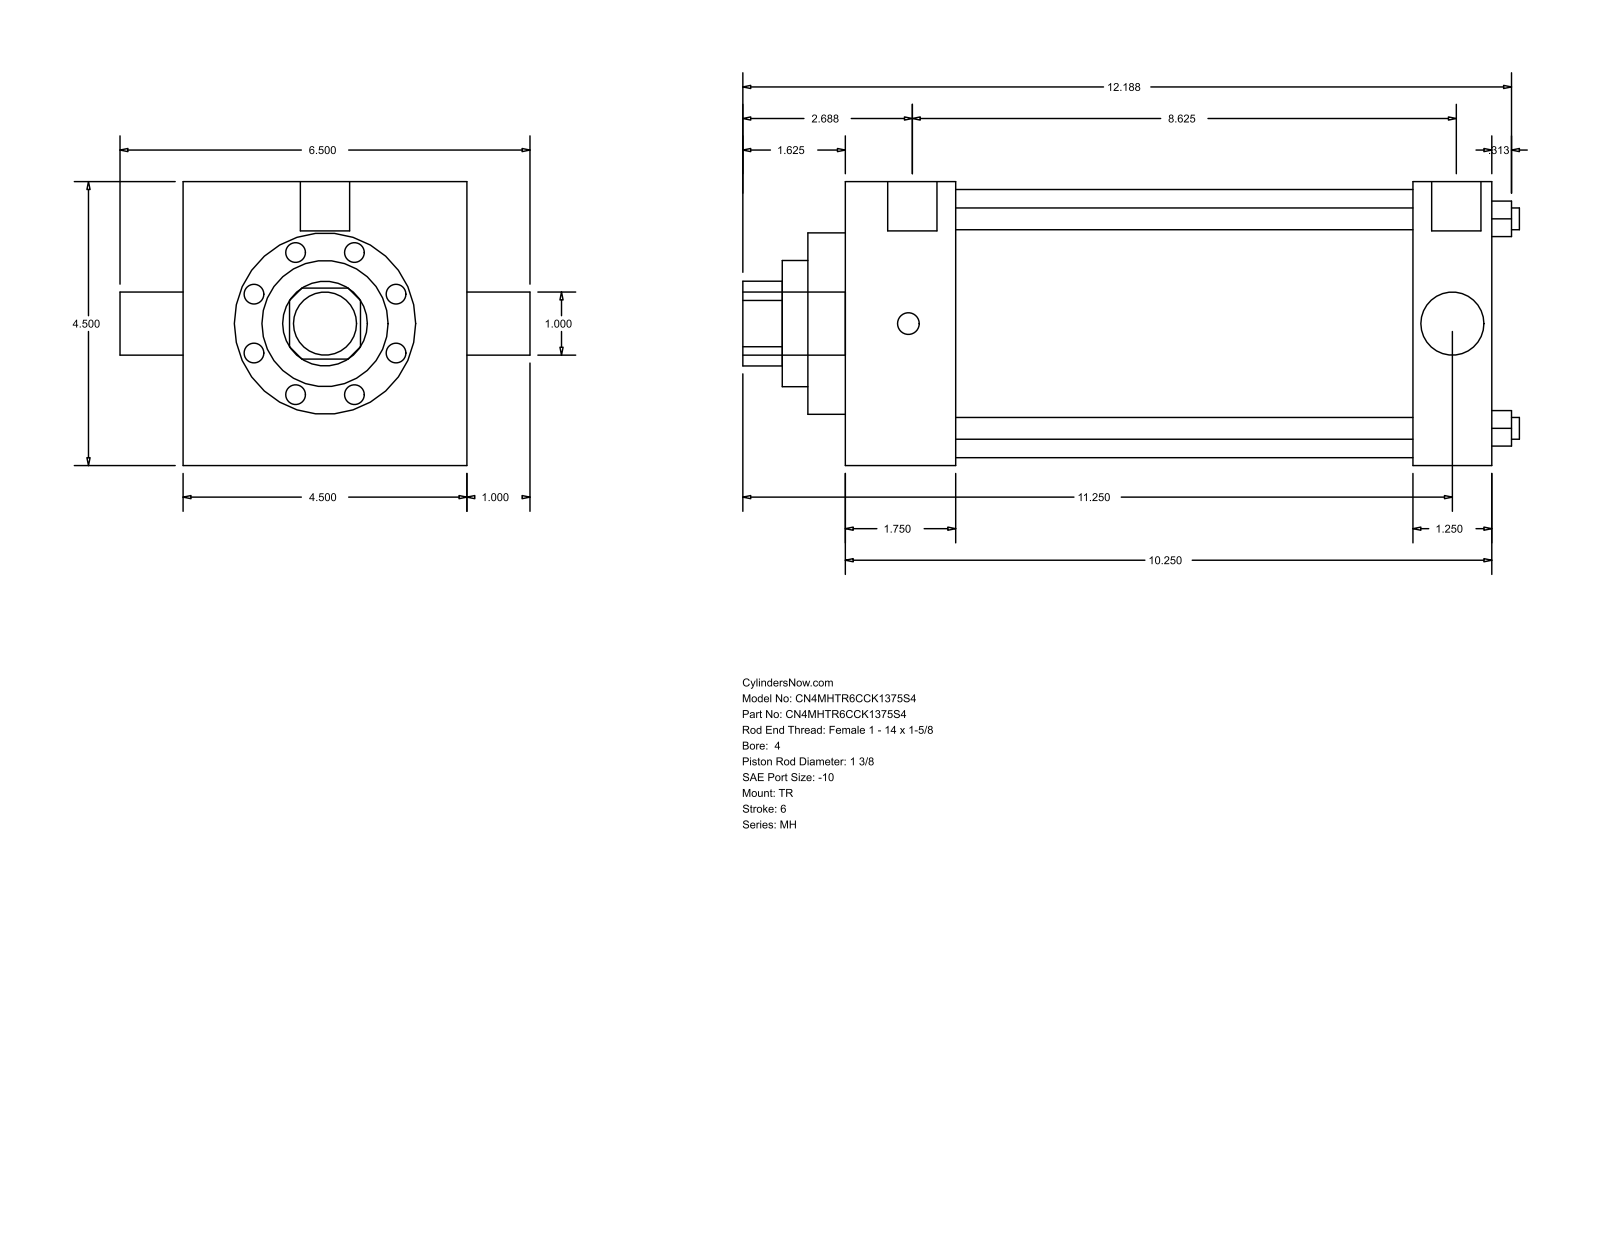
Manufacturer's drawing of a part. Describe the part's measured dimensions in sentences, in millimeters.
The part is named "MH_TR__0400_1.375". Its 3-D file was written by "GSSL Pune (CONFIG_CONTROL_DESIGN)". It is 0 solids with 86 faces: 61 planar, 25 cylindrical and 0 other. Overall it measures 312.74 by 165.1 by 114.3 millimeters. Round holes: 4 of diameter 8.76, 1 of diameter 25.4, 1 of diameter 34.92, 1 of diameter 50.8, 1 of diameter 73.03, 1 of diameter 107.95. Round bosses or shafts: 3 of diameter 8.73, 2 of diameter 19.84, 1 of diameter 25.4. Partial cylindrical surfaces (rounded edges, fillets, slot ends): 1 of radius 17.06. The main face-to-face distances are 114.3, 260.35, 44.45, 215.9, 228.61, 184.16, 31.74, 15.08, 59.53, 243.69. The hole center spacings are 59.62, 84.32, 119.25.
